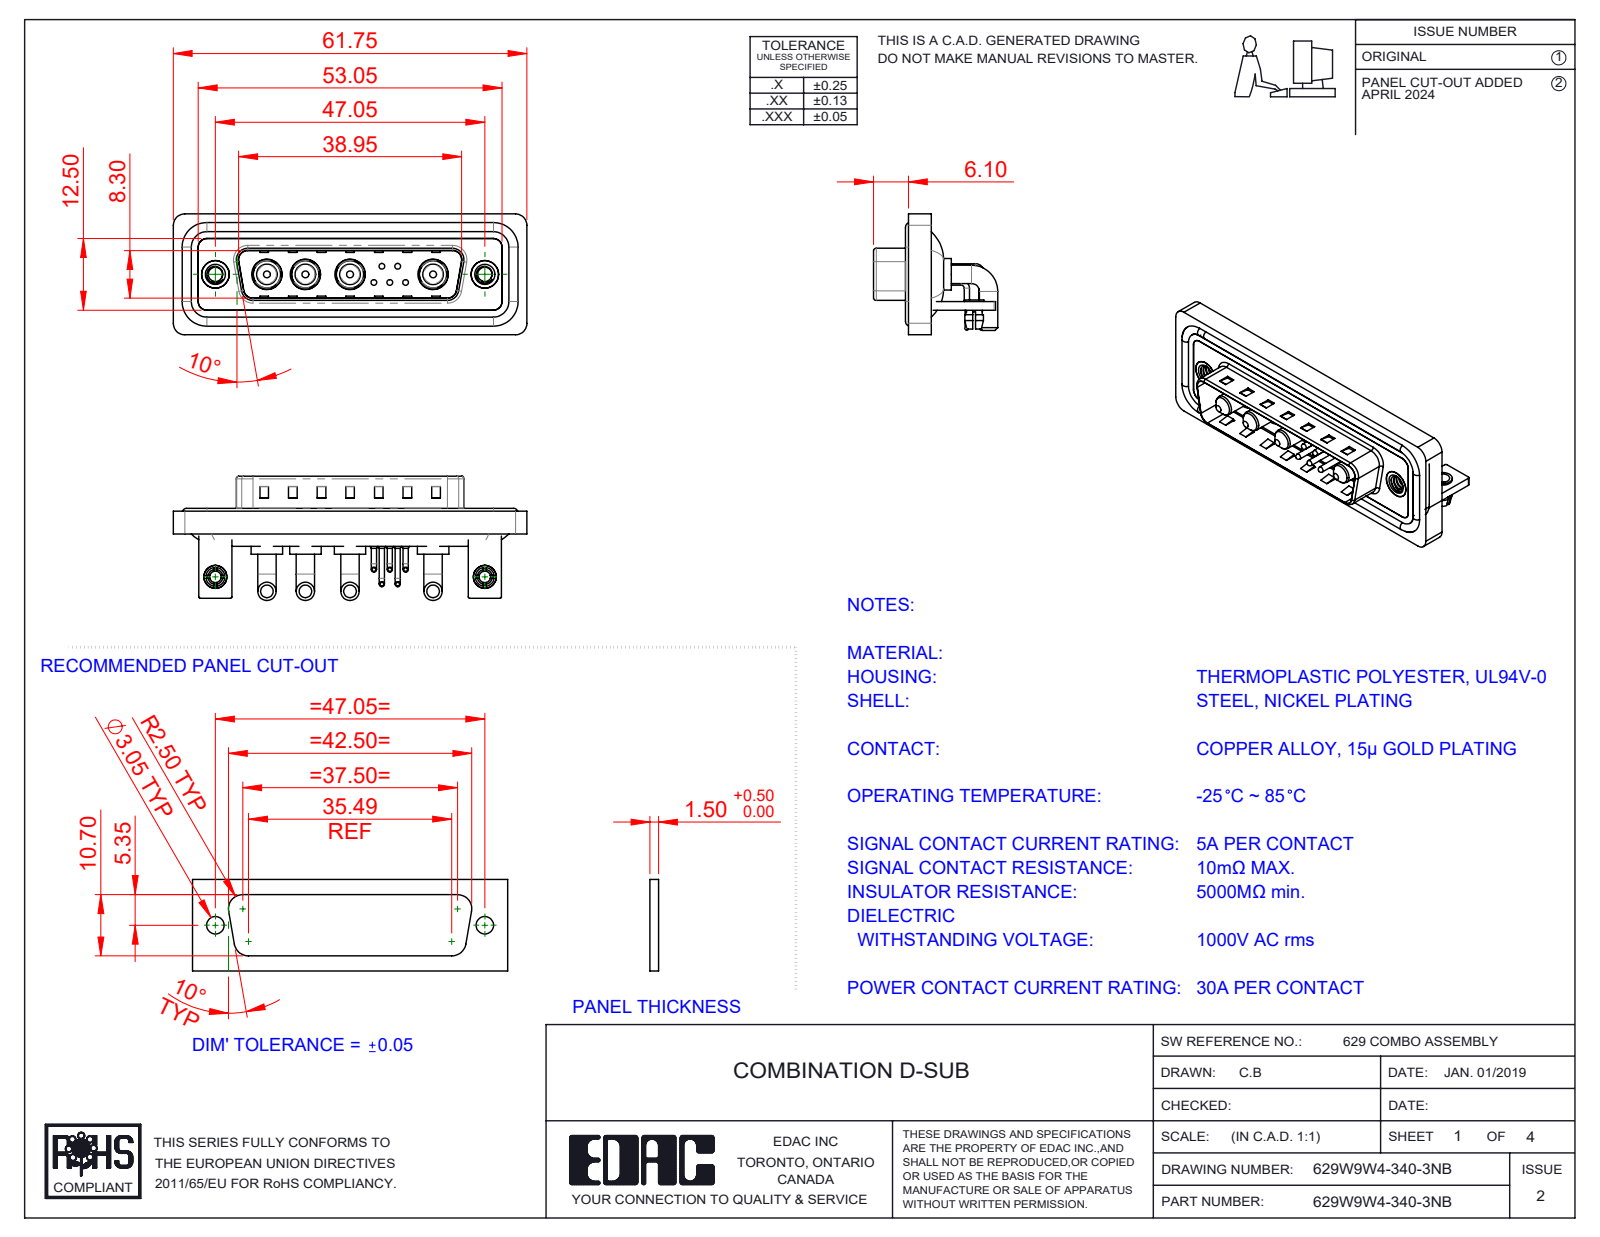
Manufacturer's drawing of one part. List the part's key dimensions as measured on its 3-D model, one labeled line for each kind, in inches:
Part name (STEP PRODUCT): 629Combo Contact Row 2; 629Combo Stabilizer Bracket; 629Combo Contact Row 1; 629Combo Shell Front_25 Contacts (+7 more)
STEP written by: SolidWorks 2023 (CONFIG_CONTROL_DESIGN)
Units: inches
Bodies: 24 solids, 1335 faces (637 planar, 502 cylindrical, 196 other)
Overall size (bounding box): 2.431 × 0.854 × 0.831
Volume: 0.496 in³ · Surface area: 20.54 in²
Round holes (diameter × count): ⌀0.079 ×7, ⌀0.03 ×5, ⌀0.063 ×5, ⌀0.098 ×4, ⌀0.191 ×4, ⌀0.209 ×4, ⌀0.126 ×2, ⌀0.157 ×2, ⌀0.189 ×2, ⌀0.197 ×2
Round bosses / shafts (diameter × count): ⌀0.035 ×10, ⌀0.126 ×8, ⌀0.059 ×5, ⌀0.039 ×5, ⌀0.026 ×5, ⌀0.217 ×4, ⌀0.205 ×4, ⌀0.187 ×4
Partial cylindrical surfaces — rounded edges, fillets, slot ends (radius × count): R0.079 ×19, R0.059 ×18, R0.01 ×16, R0.02 ×9, R0.063 ×8, R0.04 ×5, R0.024 ×4, R0.026 ×4
Main face-to-face distances: 0.016, 0.059, 0.031, 0.114, 0.083, 0.043, 0.146, 0.161, 0.177, 0.063
Hole centre spacings: 0.124, 0.109, 0.198, 0.571, 1.852, 0.109, 0.173, 0.174
